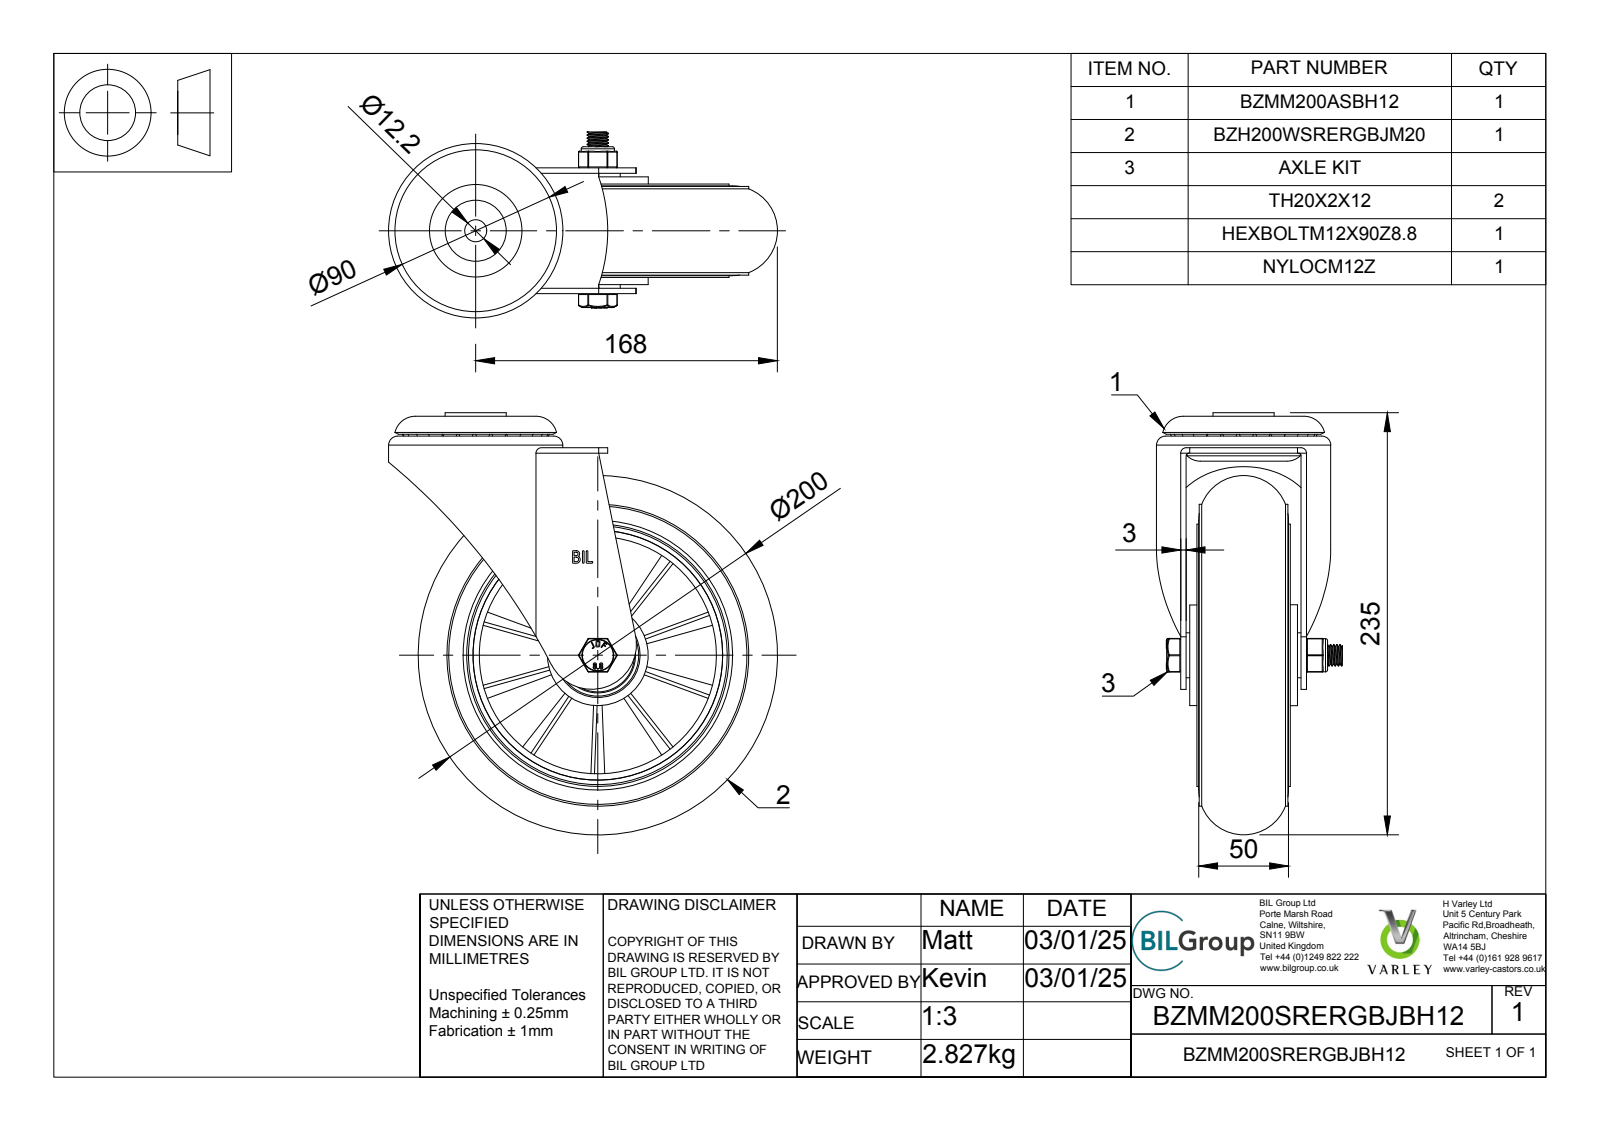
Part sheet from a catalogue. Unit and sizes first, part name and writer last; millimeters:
Units: millimetres
Overall size (bounding box): 235 × 216.5 × 103.5
Round holes (diameter × count): ⌀12.2 ×2, ⌀12 ×1, ⌀12.3 ×1, ⌀14 ×1, ⌀20 ×1, ⌀28.5 ×1, ⌀30.8 ×1, ⌀40.3 ×1, ⌀40.5 ×1, ⌀42 ×1, ⌀47 ×1, ⌀51 ×1
Round bosses / shafts (diameter × count): ⌀24 ×2, ⌀168 ×1, ⌀146 ×1, ⌀97 ×1, ⌀63 ×1, ⌀56.2 ×1, ⌀56 ×1, ⌀40.8 ×1
Partial cylindrical surfaces — rounded edges, fillets, slot ends (radius × count): R0.5 ×19, R0.47 ×4, R0.9 ×4, R1.5 ×4, R0.89 ×2, R0.89 ×2, R3 ×2, R6.78 ×2
Main face-to-face distances: 3, 14.25, 2, 47.75, 67, 17.25, 52.75, 49.75, 19.25, 50.75
Volume: 1 034 000 mm³ · Surface area: 327 378 mm²
Bodies: 81 solids, 1156 faces (439 planar, 205 cylindrical, 512 other)
Part name (STEP PRODUCT): BZMM200SRERGBJBH12 v3; BZMM200ASBH12 - 64 v1; ZINC PLATED, PRESSED STEEL HEAD; ZINC PLATED, PRESSED STEEL HEAD Geometry (+6 more)
STEP written by: Autodesk Translation Framework v13.20.0.188 (AP242_MANAGED_MODEL_BASED_3D_ENGINEERING_MIM_LF)
